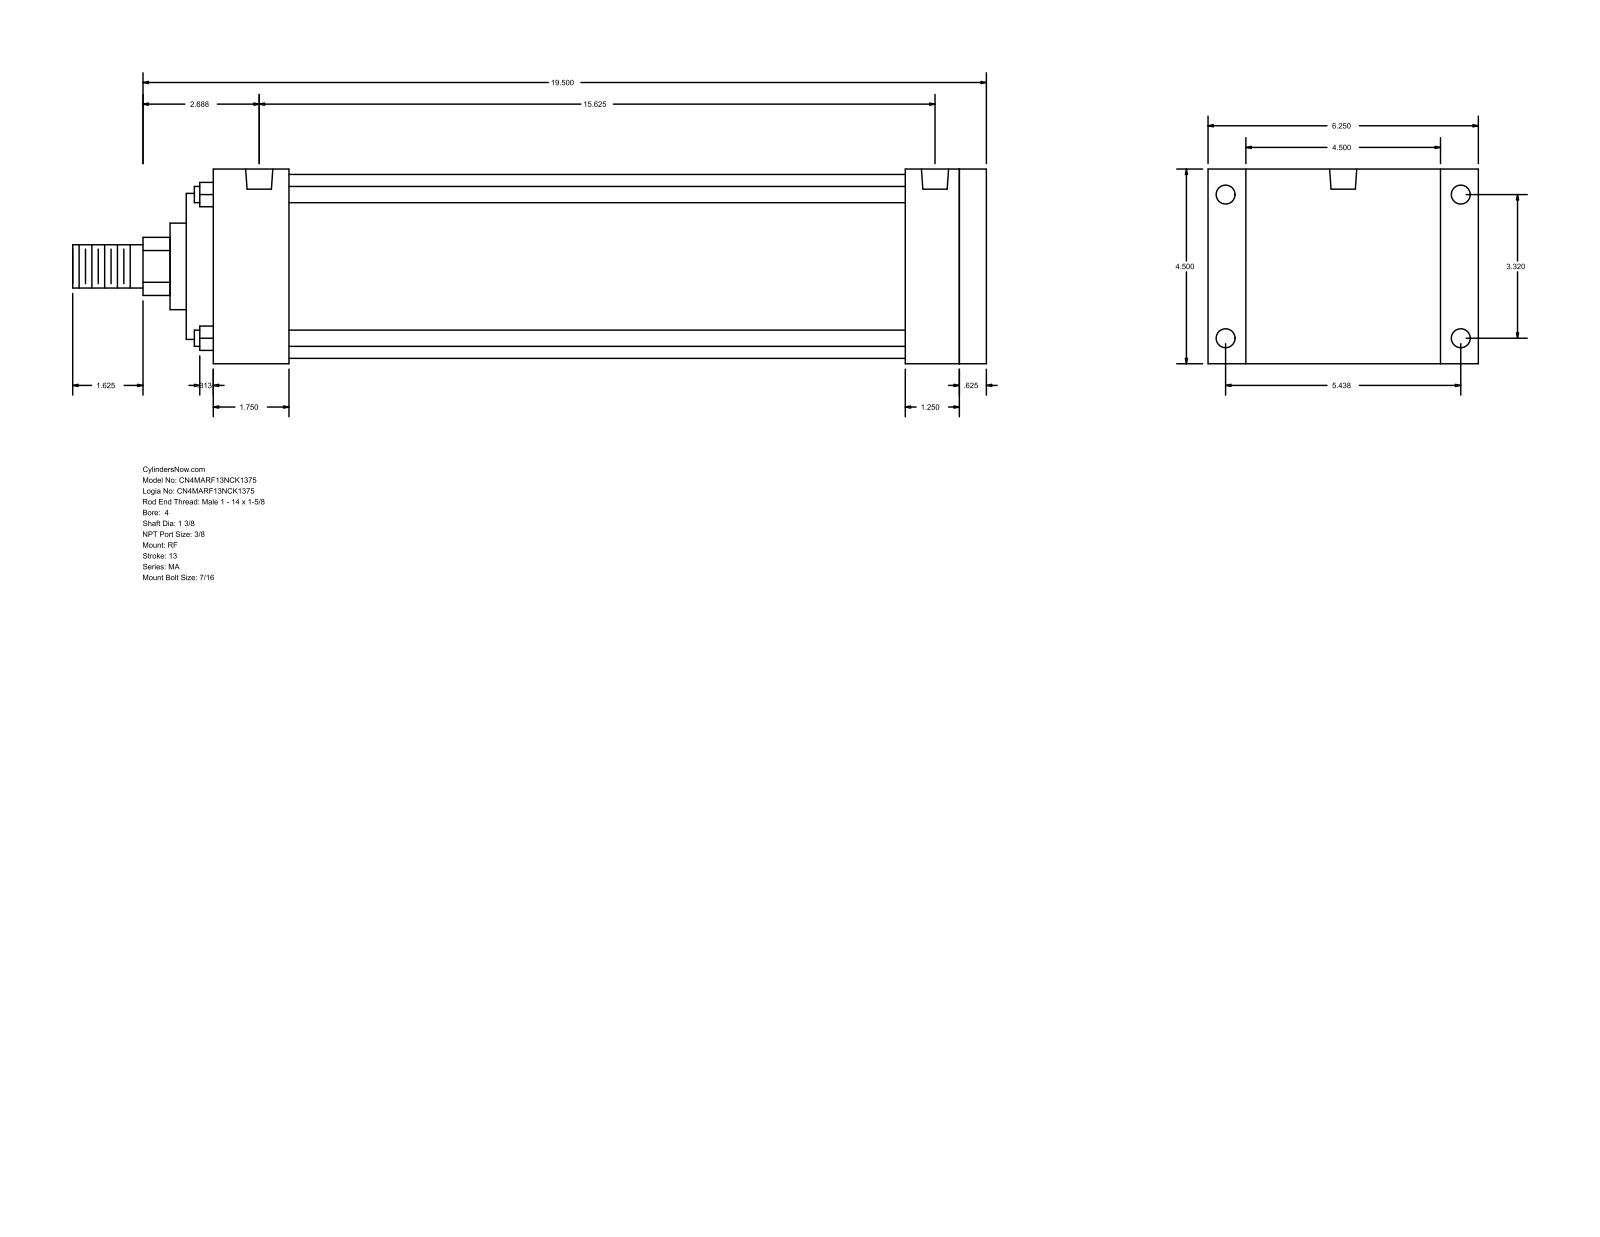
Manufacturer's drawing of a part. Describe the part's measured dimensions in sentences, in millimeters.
The part is named "MA_RF__0400_1.375". Its 3-D file was written by "GSSL Pune (CONFIG_CONTROL_DESIGN)". It is 0 solids with 94 faces: 65 planar, 29 cylindrical and 0 other. Overall it measures 536.58 by 158.75 by 114.3 millimeters. Round holes: 8 of diameter 11.11, 2 of diameter 15.93. Round bosses or shafts: 4 of diameter 9.53, 1 of diameter 107.95, 1 of diameter 85.72, 1 of diameter 50.8, 1 of diameter 34.92, 1 of diameter 25.4. Partial cylindrical surfaces (rounded edges, fillets, slot ends): 1 of radius 17.06. The main face-to-face distances are 114.3, 454.03, 15.87, 438.16, 469.9, 22.23, 136.53, 422.28, 406.41, 31.75. The hole center spacings are 84.32, 138.12, 161.82, 387.35, 4.76, 4.77, 392.11, 392.12.
